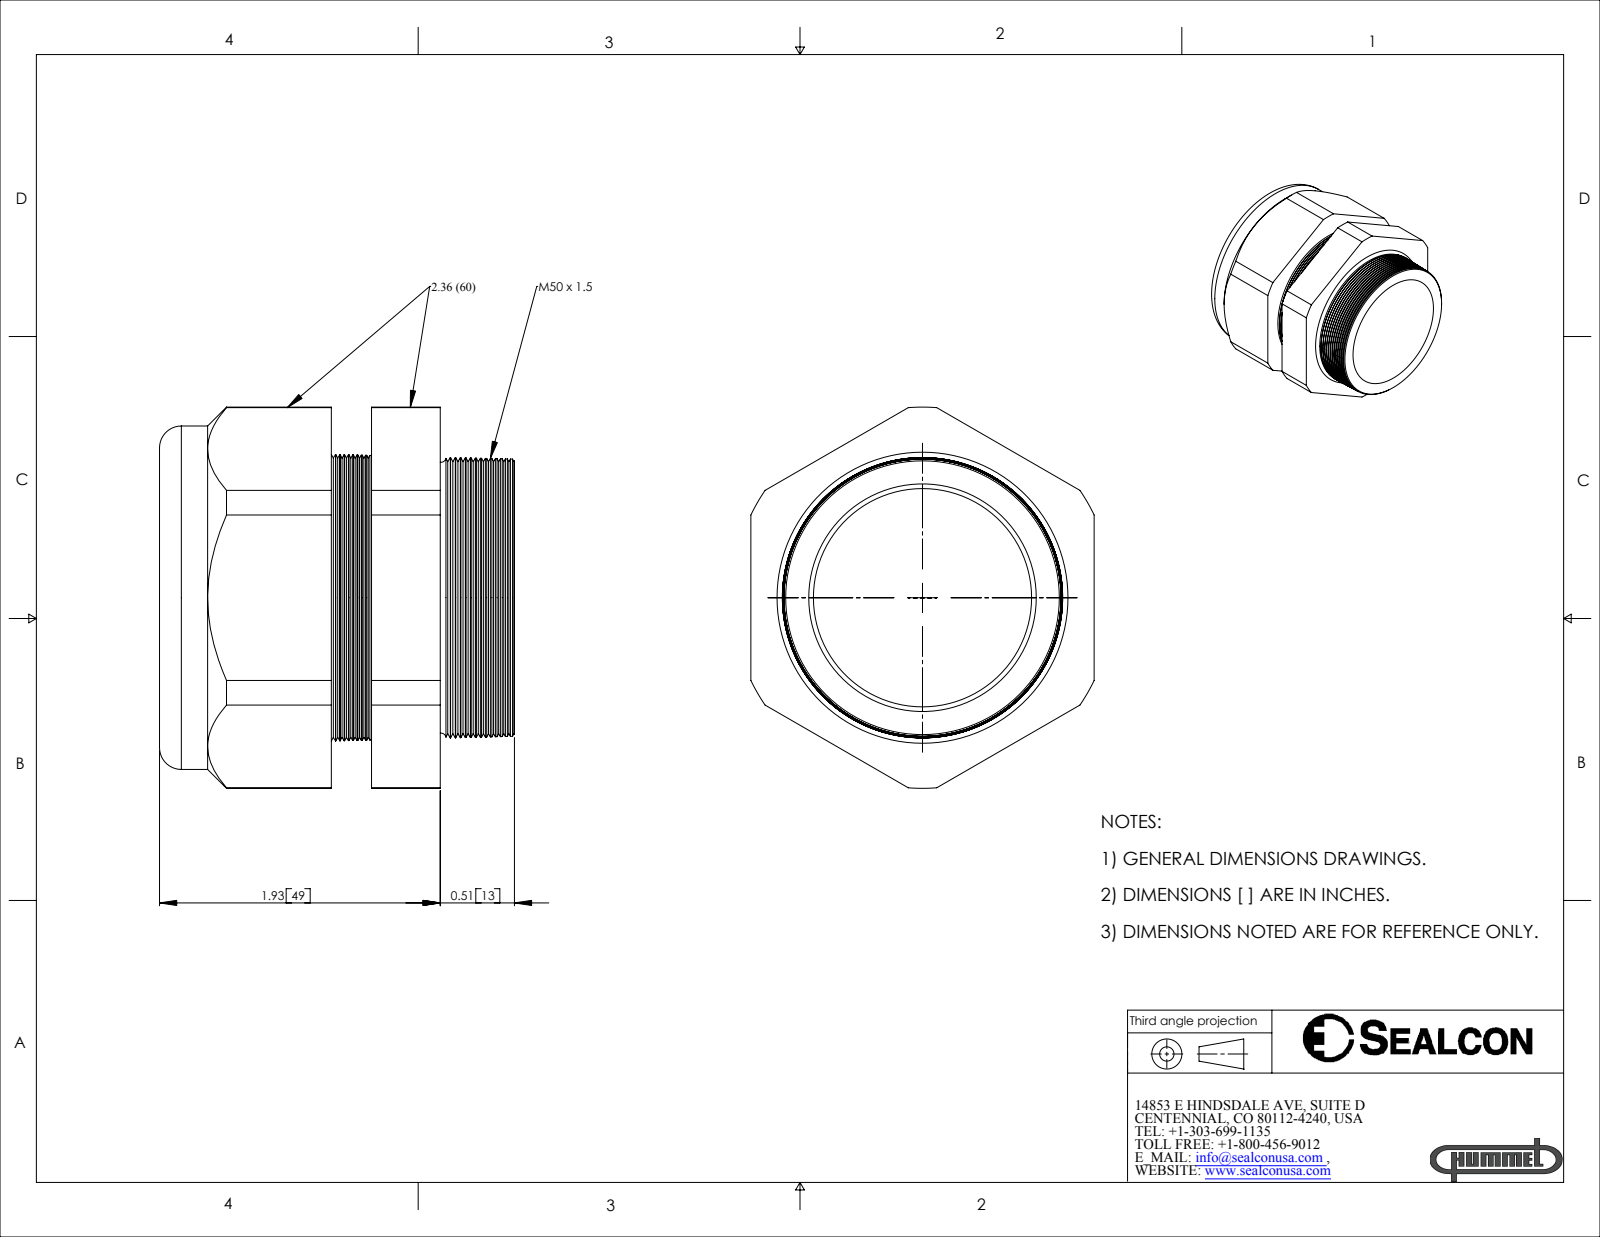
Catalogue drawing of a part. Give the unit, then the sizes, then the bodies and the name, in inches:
Units: inches
Overall size (bounding box): 2.62 × 2.44 × 2.36
Round holes (diameter × count): ⌀1.48 ×1, ⌀1.5 ×1
Round bosses / shafts (diameter × count): ⌀2.36 ×1
Partial cylindrical surfaces — rounded edges, fillets, slot ends (radius × count): R1.31 ×1
Main face-to-face distances: 2.36, 1.008, 0.731, 0.276, 0.43, 1.161, 1.438, 1.91, 1.48, 0.749
Volume: 6.336 in³ · Surface area: 47.67 in²
Bodies: 2 solids, 190 faces (20 planar, 20 cylindrical, 150 other)
Part name (STEP PRODUCT): CD50MP-BK
STEP written by: SolidWorks 2007 (CONFIG_CONTROL_DESIGN)
